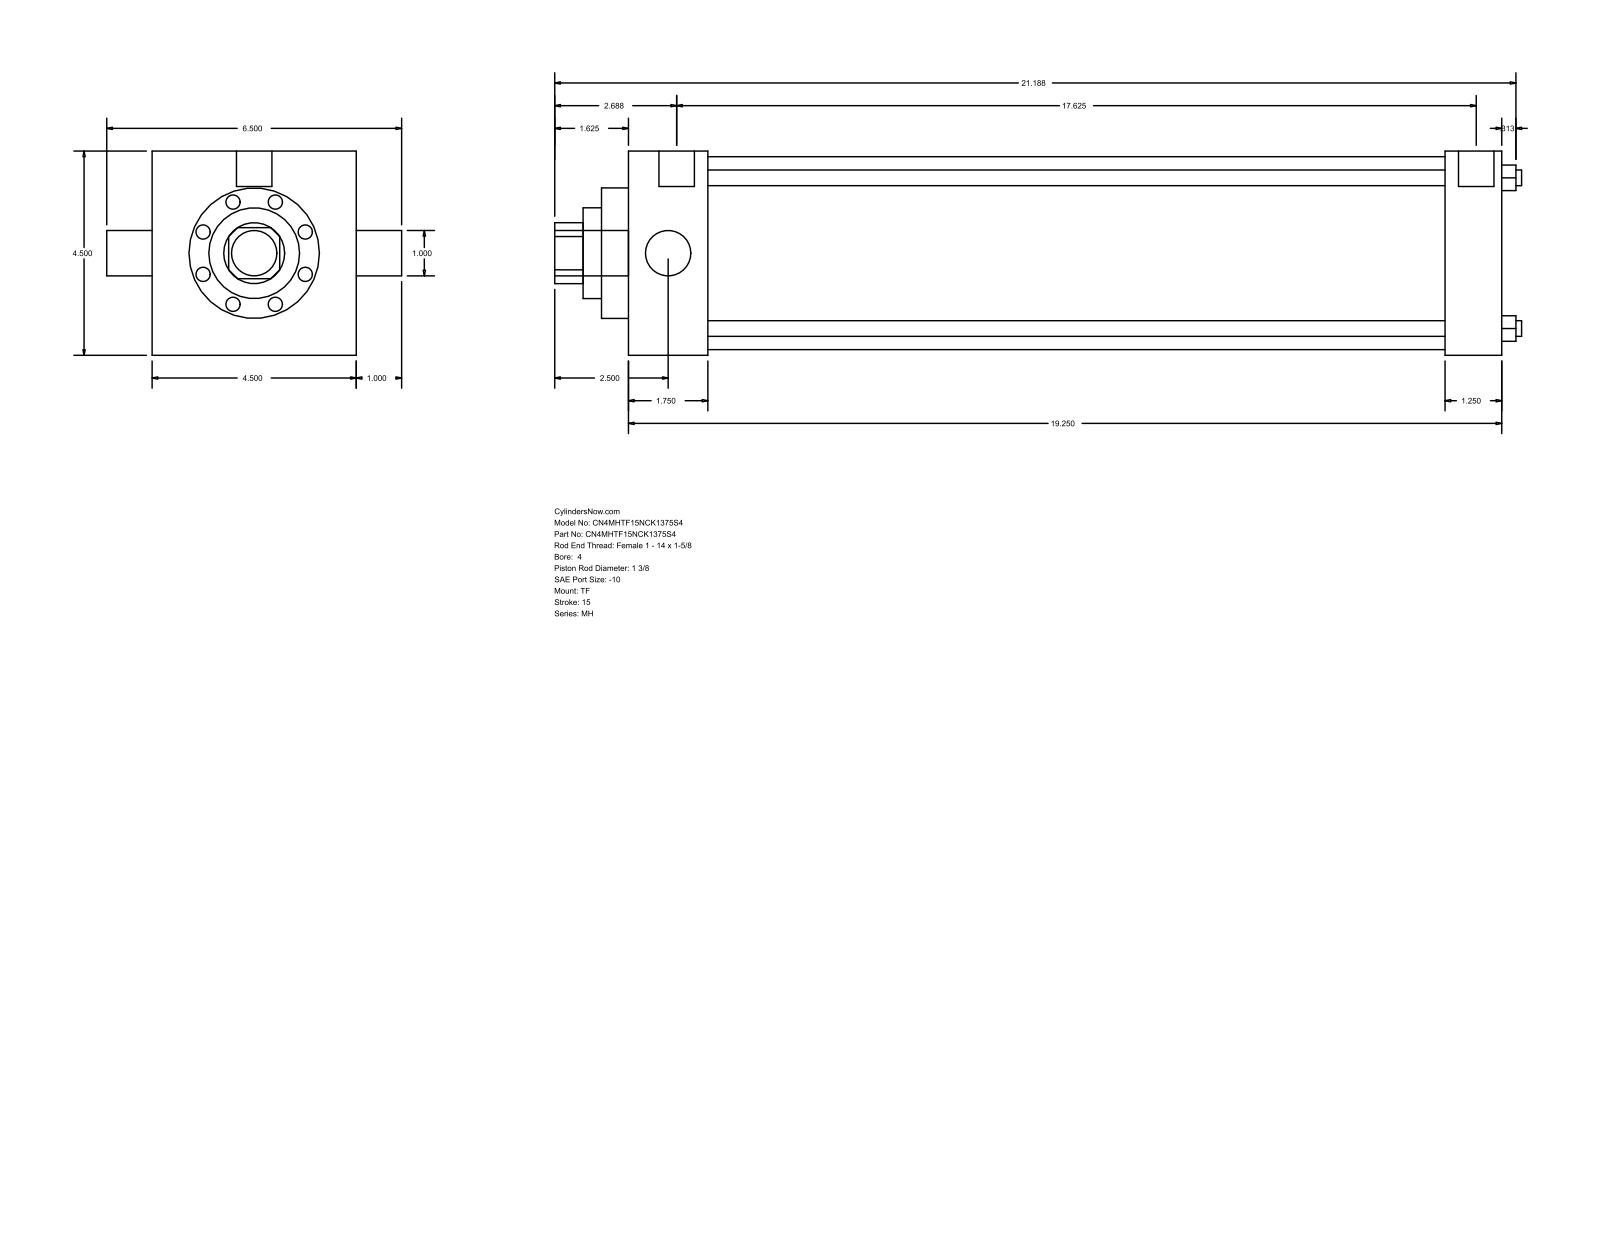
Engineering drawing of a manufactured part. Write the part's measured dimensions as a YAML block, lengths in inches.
part_name: "MH_TF__0400_1.375"
step_written_by: "GSSL Pune (CONFIG_CONTROL_DESIGN)"
units: inches
bodies: {solids: 0, faces: 86, planar: 61, cylindrical: 25, other: 0}
overall_size: [21.313, 6.5, 4.5]
round_holes:
  - {diameter: 0.345, count: 4}
  - {diameter: 1, count: 1}
  - {diameter: 1.375, count: 1}
  - {diameter: 2, count: 1}
  - {diameter: 2.875, count: 1}
  - {diameter: 4.25, count: 1}
round_bosses_or_shafts:
  - {diameter: 0.344, count: 3}
  - {diameter: 0.781, count: 2}
  - {diameter: 1, count: 1}
partial_cylinders:
  - {radius: 0.672, count: 1}
face_to_face_distances: [4.5, 19.25, 1.75, 17.5, 18, 16.25, 1.25, 0.594, 2.344, 18.594]
hole_center_spacings: [2.347, 3.32, 4.695]
